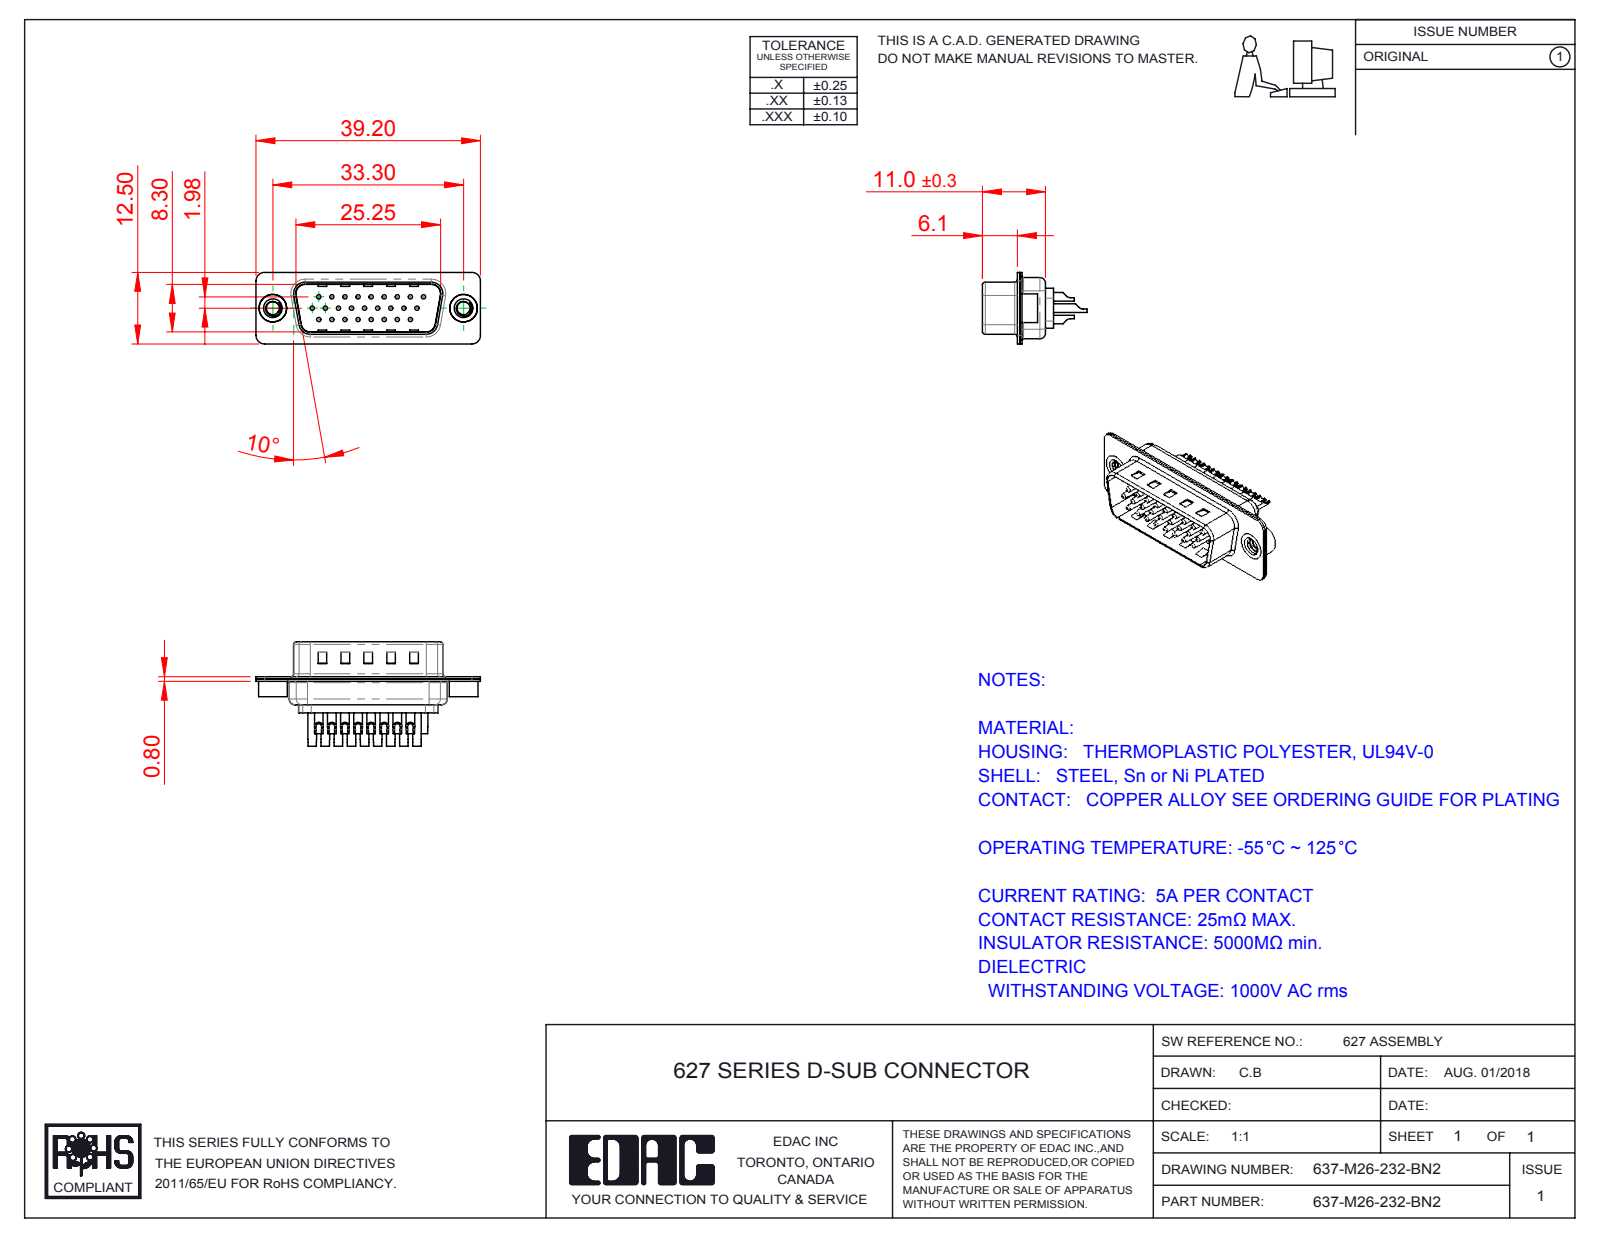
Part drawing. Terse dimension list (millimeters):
name: 637M Contact Row 3_32; 637M Shell Front_26 Contacts; 637M Contact Row 1_32; 637-M26-232-BN2 (+4 more)
written by: SolidWorks 2016 (CONFIG_CONTROL_DESIGN)
unit: mm
bodies: 31 solids, 1302 faces (373 planar, 549 cylindrical, 380 other)
size: 39.2 × 18.25 × 12.5
volume: 1 996 mm³; area: 6 073 mm²
holes: 26× ⌀0.75, 26× ⌀1, 26× ⌀1.6, 26× ⌀2, 2× ⌀2.26, 2× ⌀4, 2× ⌀4.8
bosses: 26× ⌀1.5, 2× ⌀5, 2× ⌀4.9
rounds: 16× R1.5, 12× R2, 8× R0.5, 8× R1.6, 7× R1, 4× R0.25, 4× R0.6, 4× R0.65
face distances: 0.4, 0.8, 9.5, 9.1, 8.7, 9.9, 0.75, 0.35, 1.2, 1.1
hole spacings: 3.96, 2.28, 4.57, 6.05, 2.29, 8.24, 6.86, 10.48
